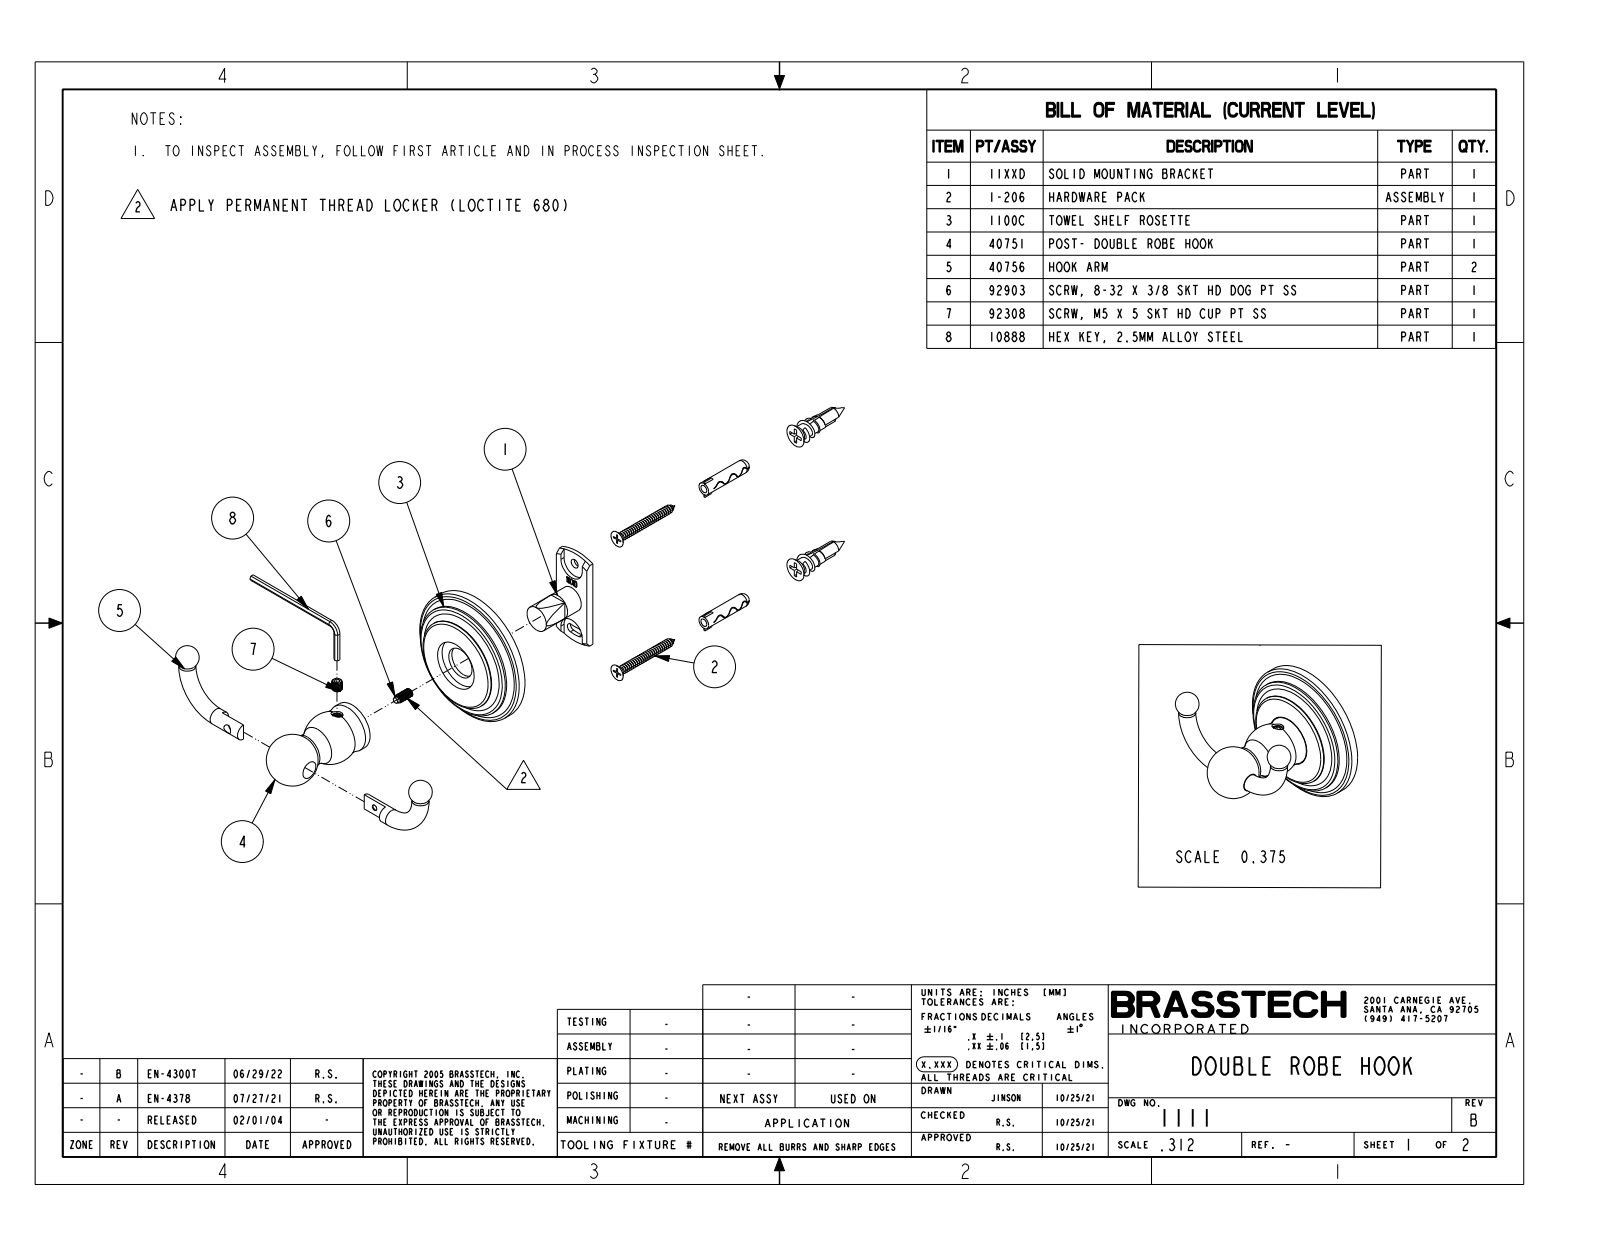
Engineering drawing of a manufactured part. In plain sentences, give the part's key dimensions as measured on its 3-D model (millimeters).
The part is named "1111". Its 3-D file was written by "CREO PARAMETRIC BY PTC INC, 2018400 (AUTOMOTIVE_DESIGN)". It is 1 solid with 42 faces: 4 planar, 10 cylindrical and 28 other. Overall it measures 71.5 by 65 by 61.5 millimeters. Its volume is 53 910 cubic millimeters and its surface area 13 520 square millimeters. Round bosses or shafts: 2 of diameter 8, 1 of diameter 65, 1 of diameter 55.4, 1 of diameter 44.4. The main face-to-face distances are 13, 9.2, 3.8, 4.8, 4.4, 8.2.
